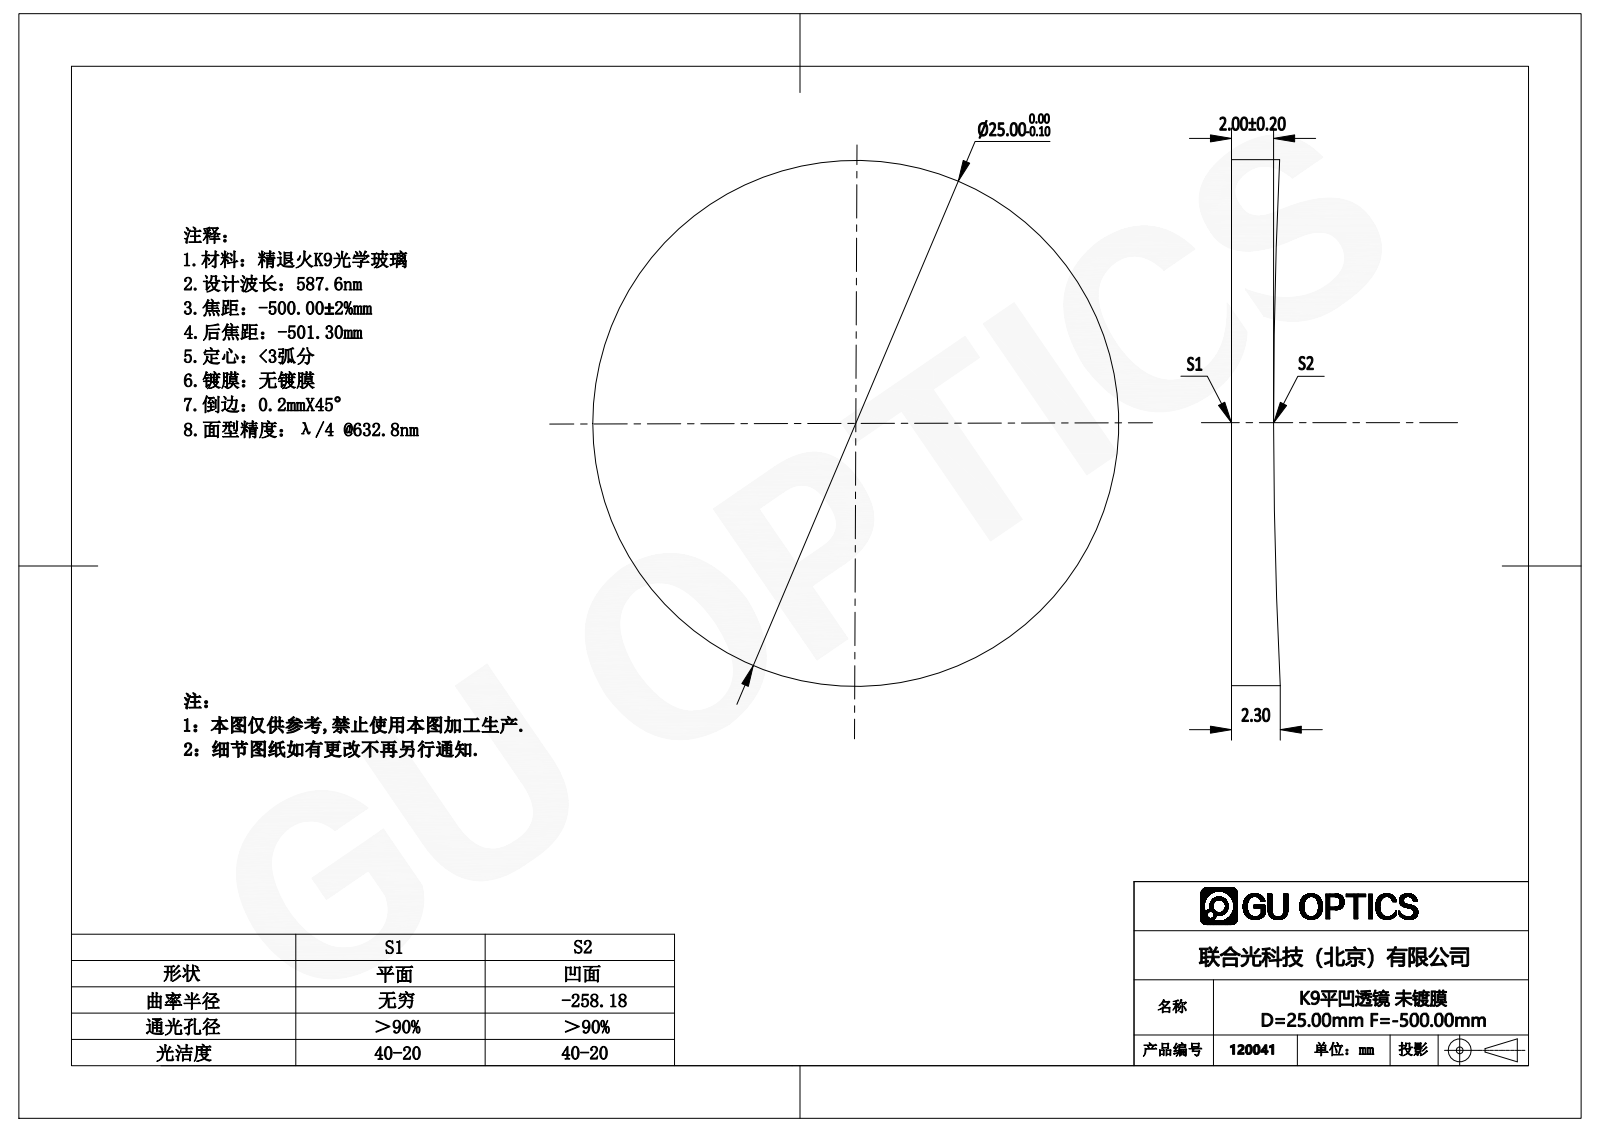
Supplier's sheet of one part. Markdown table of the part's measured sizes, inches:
| quantity | value |
| --- | --- |
| part name | 120041 |
| STEP written by | SolidWorks 2016 (AUTOMOTIVE_DESIGN) |
| units | inches |
| bodies | 1 solid, 5 faces (1 planar, 2 cylindrical, 2 other) |
| overall size | 0.984 × 0.984 × 0.09 |
| volume | 0.064 in³ |
| surface area | 1.801 in² |
| round bosses / shafts (diameter × count) | 0.984 × 1 |
